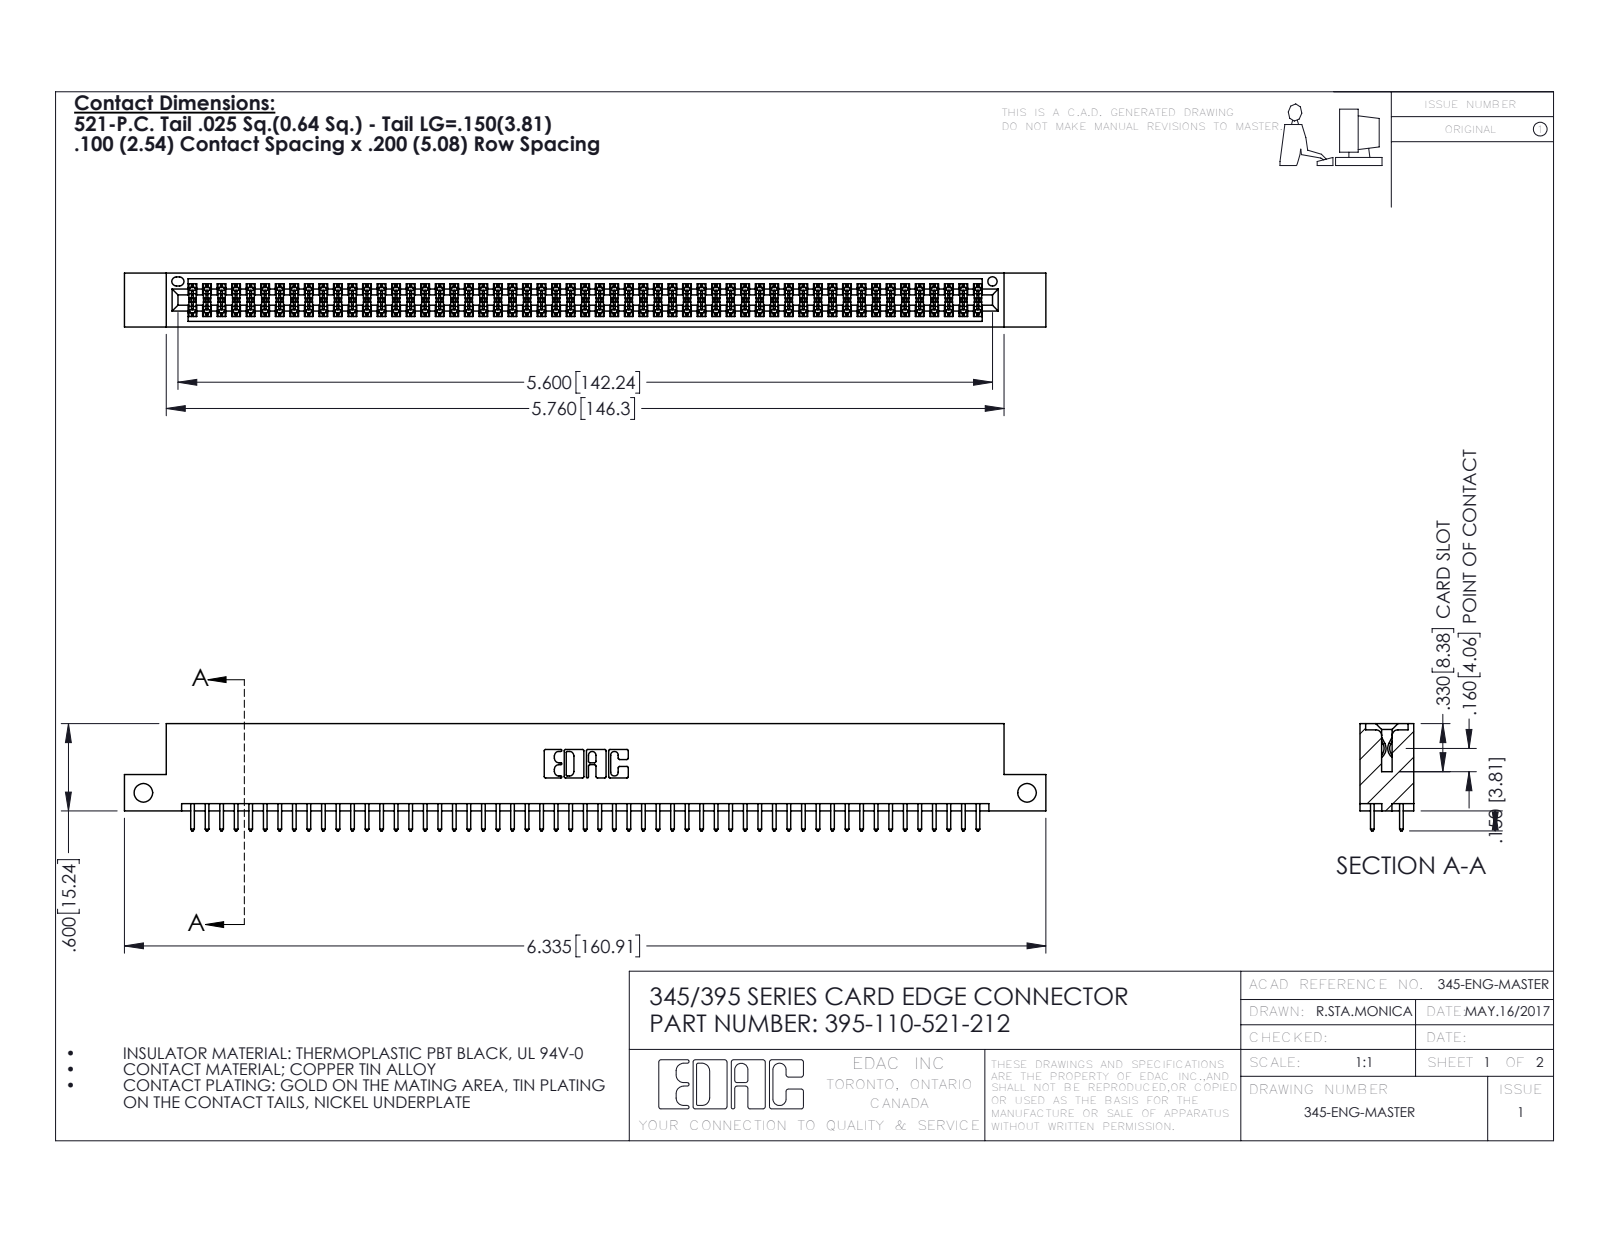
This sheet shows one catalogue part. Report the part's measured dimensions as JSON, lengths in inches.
{"part_name": "395-110-521-212; 345-292-001_345-293-121; 345 Part_Flush Mounting Lugs - Side Mount", "step_written_by": "SolidWorks 2016 (CONFIG_CONTROL_DESIGN)", "units": "inches", "bodies": {"solids": 111, "faces": 5626, "planar": 3710, "cylindrical": 1916, "other": 0}, "overall_size": [6.335, 0.737, 0.37], "volume_in3": 0.953, "surface_area_in2": 35.51, "round_holes": [[0.128, 2], [0.064, 1]], "partial_cylinders_radius": [[0.006, 165], [0.01, 110], [0.01, 22], [0.007, 6], [0.031, 6], [0.026, 3], [0.014, 2], [0.019, 2]], "face_to_face_distances": [0.298, 0.072, 0.2, 0.098, 0.272, 0.025, 0.37, 0.225, 0.175, 0.149], "hole_center_spacings": [6.075]}
